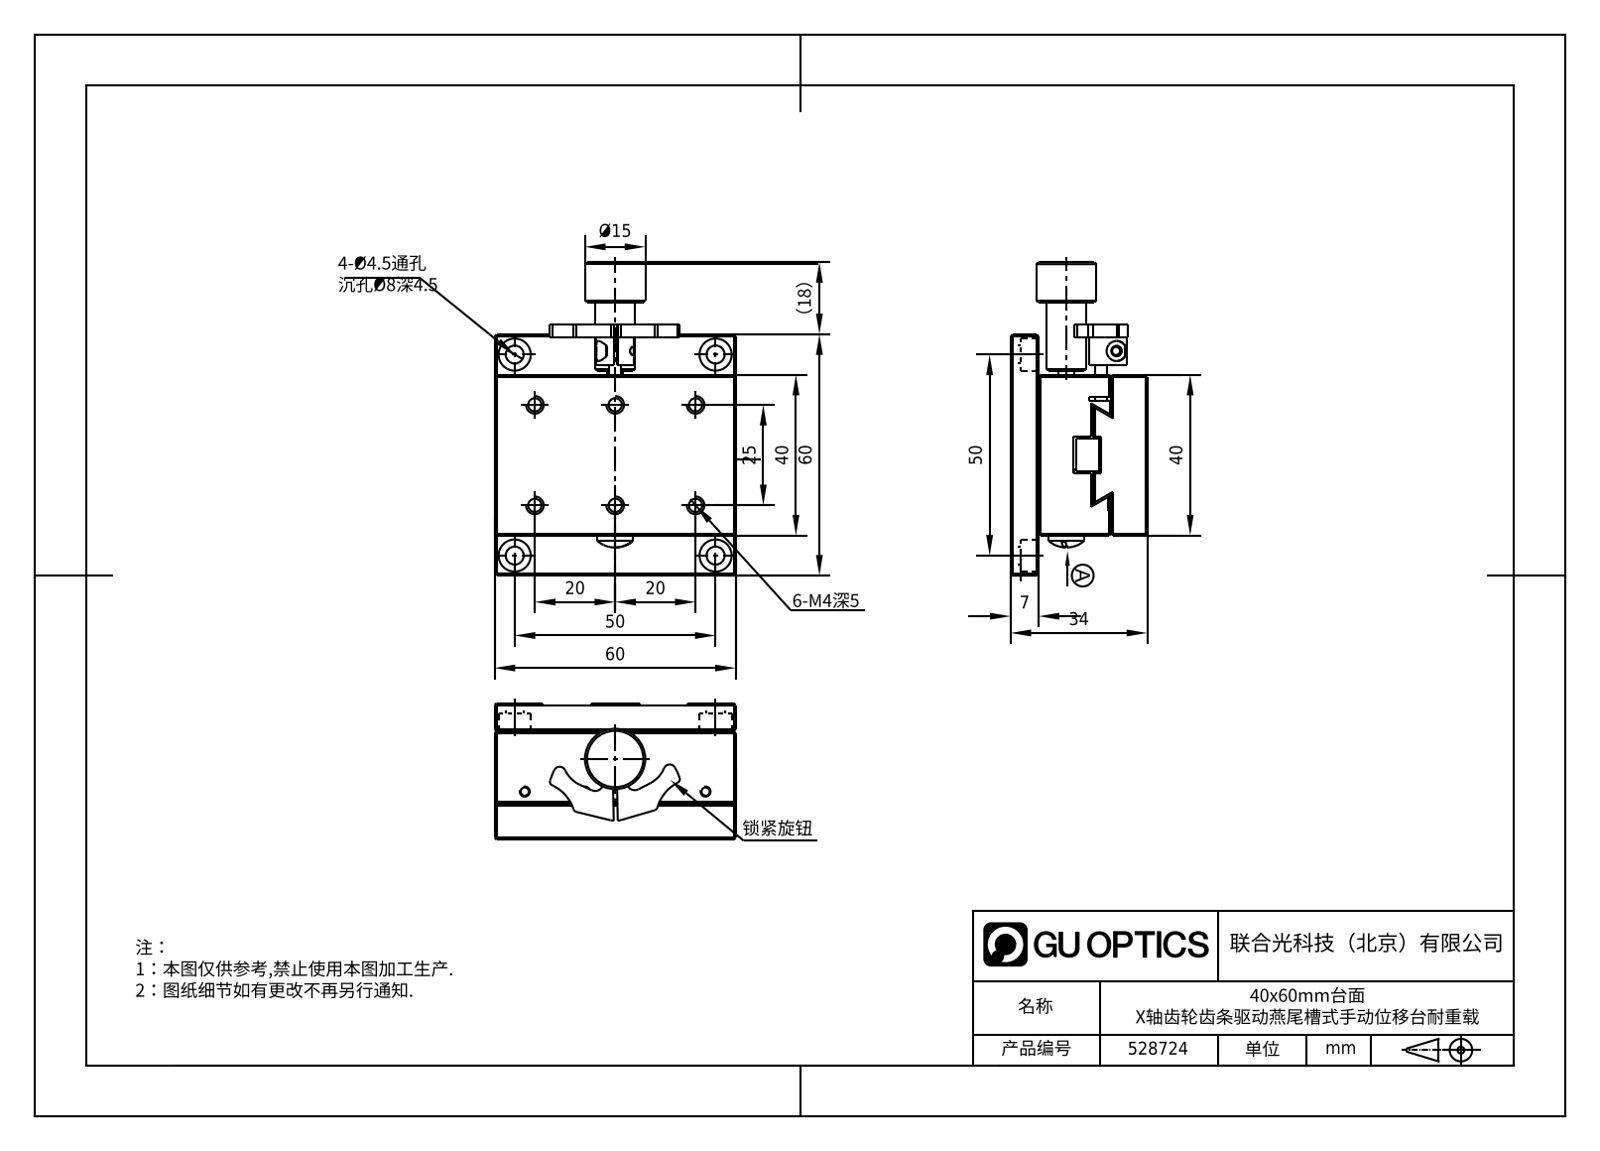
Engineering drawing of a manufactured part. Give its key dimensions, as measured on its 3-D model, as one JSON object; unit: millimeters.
{"part_name": "528724", "step_written_by": "SolidWorks 2020 (CONFIG_CONTROL_DESIGN)", "units": "millimeters", "bodies": {"solids": 6, "faces": 539, "planar": 268, "cylindrical": 125, "other": 146}, "overall_size": [81.1, 60, 34], "volume_mm3": 87085, "surface_area_mm2": 35420, "round_holes": [[3.24, 8], [8, 6], [2.46, 4], [4.5, 4], [5, 3], [2.01, 2], [2.46, 2], [2.8, 2], [4.2, 2], [2.5, 1], [2.6, 1], [3.3, 1]], "round_bosses_or_shafts": [[10, 1], [9, 1], [8, 1], [6.5, 1], [5.83, 1], [3, 1]], "partial_cylinders_radius": [[1, 4], [1.5, 2], [2, 2], [6, 2], [7.6, 2], [10, 2], [4.7, 1], [5, 1]], "face_to_face_distances": [0.5, 34, 24.5, 27, 6.5, 9, 18, 20, 13.5, 7], "hole_center_spacings": [27.95, 45.07, 13.46, 13.87, 14.58, 17.68, 20, 25]}
